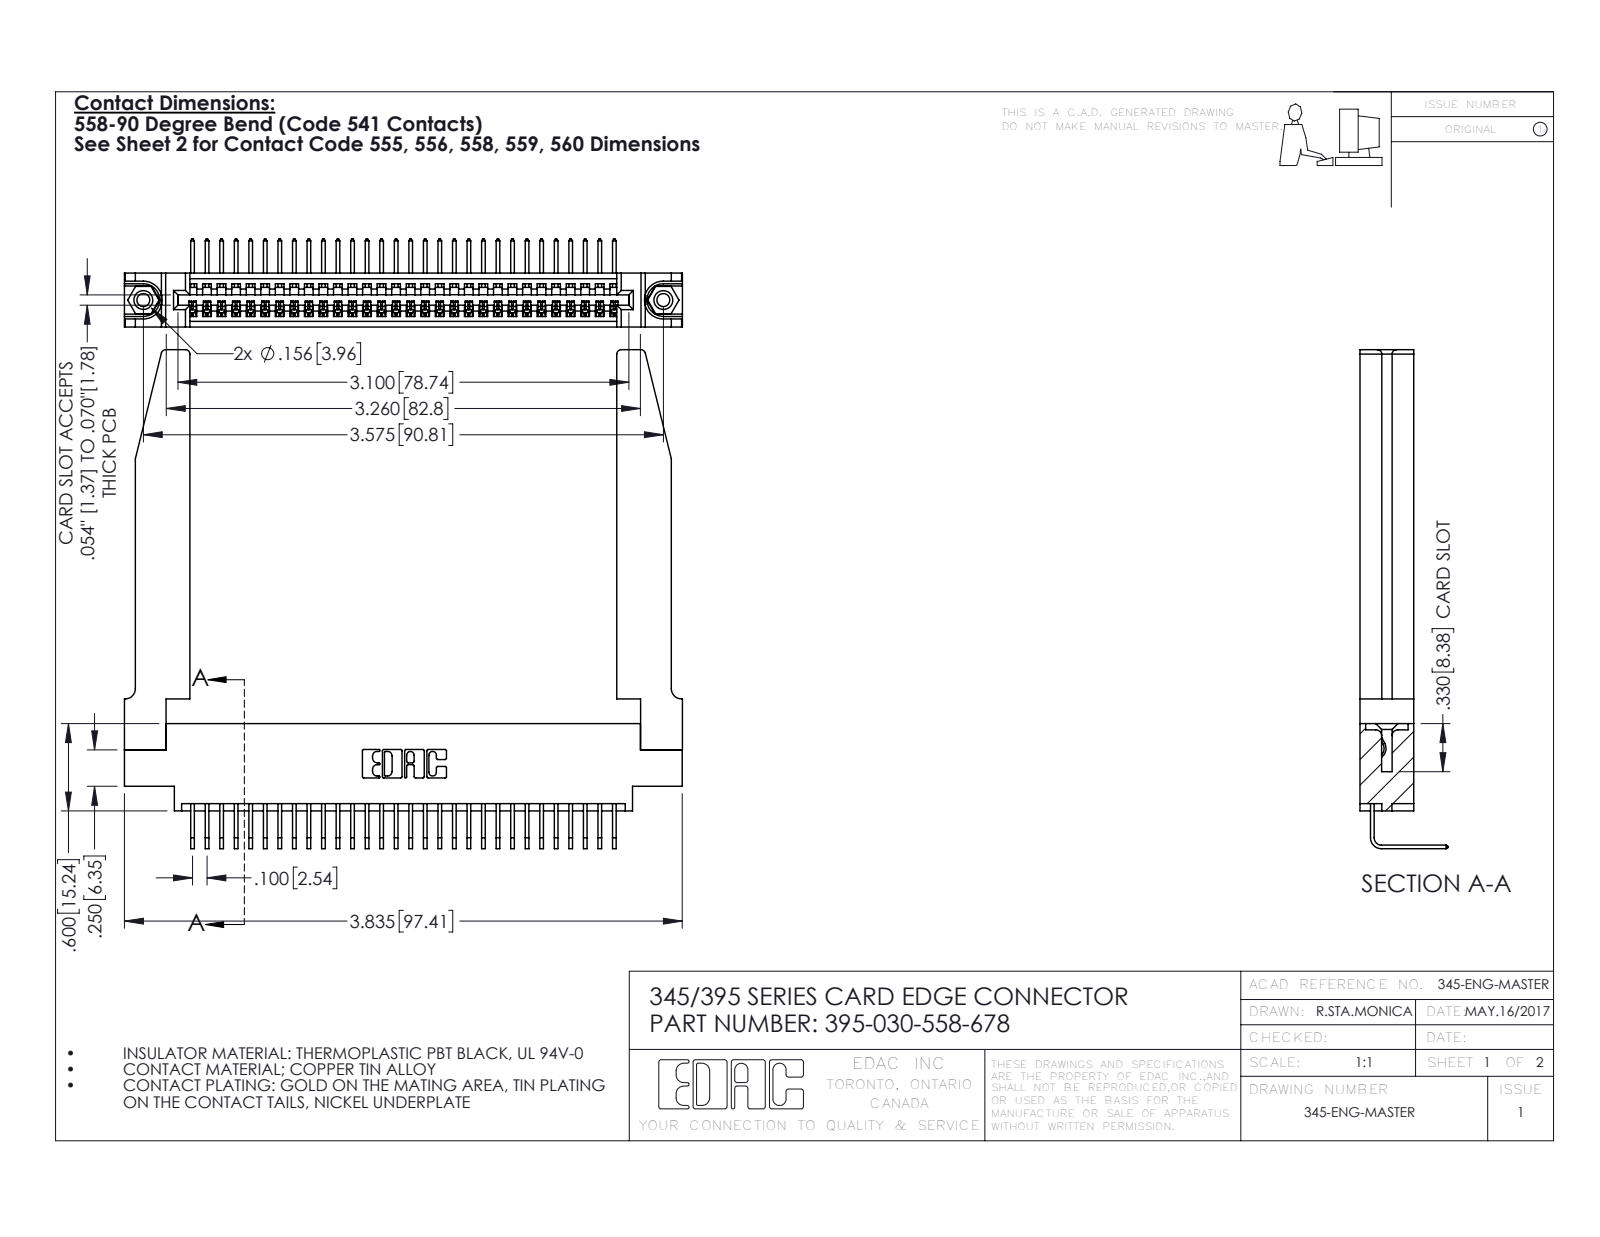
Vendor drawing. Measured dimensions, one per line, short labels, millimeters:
name: 345-292-001_558 Tail - 2; 345-250-001_345-250-001-102; 395-030-558-678; 345-220-078_345-220-078 (+1 more)
written by: SolidWorks 2016 (CONFIG_CONTROL_DESIGN)
unit: mm
bodies: 35 solids, 2164 faces (1486 planar, 626 cylindrical, 52 other)
size: 97.4 × 87.1 × 15.4
volume: 16 910 mm³; area: 19 550 mm²
holes: 2× ⌀2.3, 2× ⌀3.2, 2× ⌀4, 1× ⌀1.6
bosses: 2× ⌀3.9
rounds: 60× R0.2, 22× R0.3, 8× R0.8, 6× R0.2, 6× R0.8, 3× R0.7, 2× R0.8, 2× R1
face distances: 9.4, 1.8, 7.6, 2.5, 6.9, 0.6, 5.1, 3.8, 3.8, 5.7
hole spacings: 6.9, 84.8, 90.8
